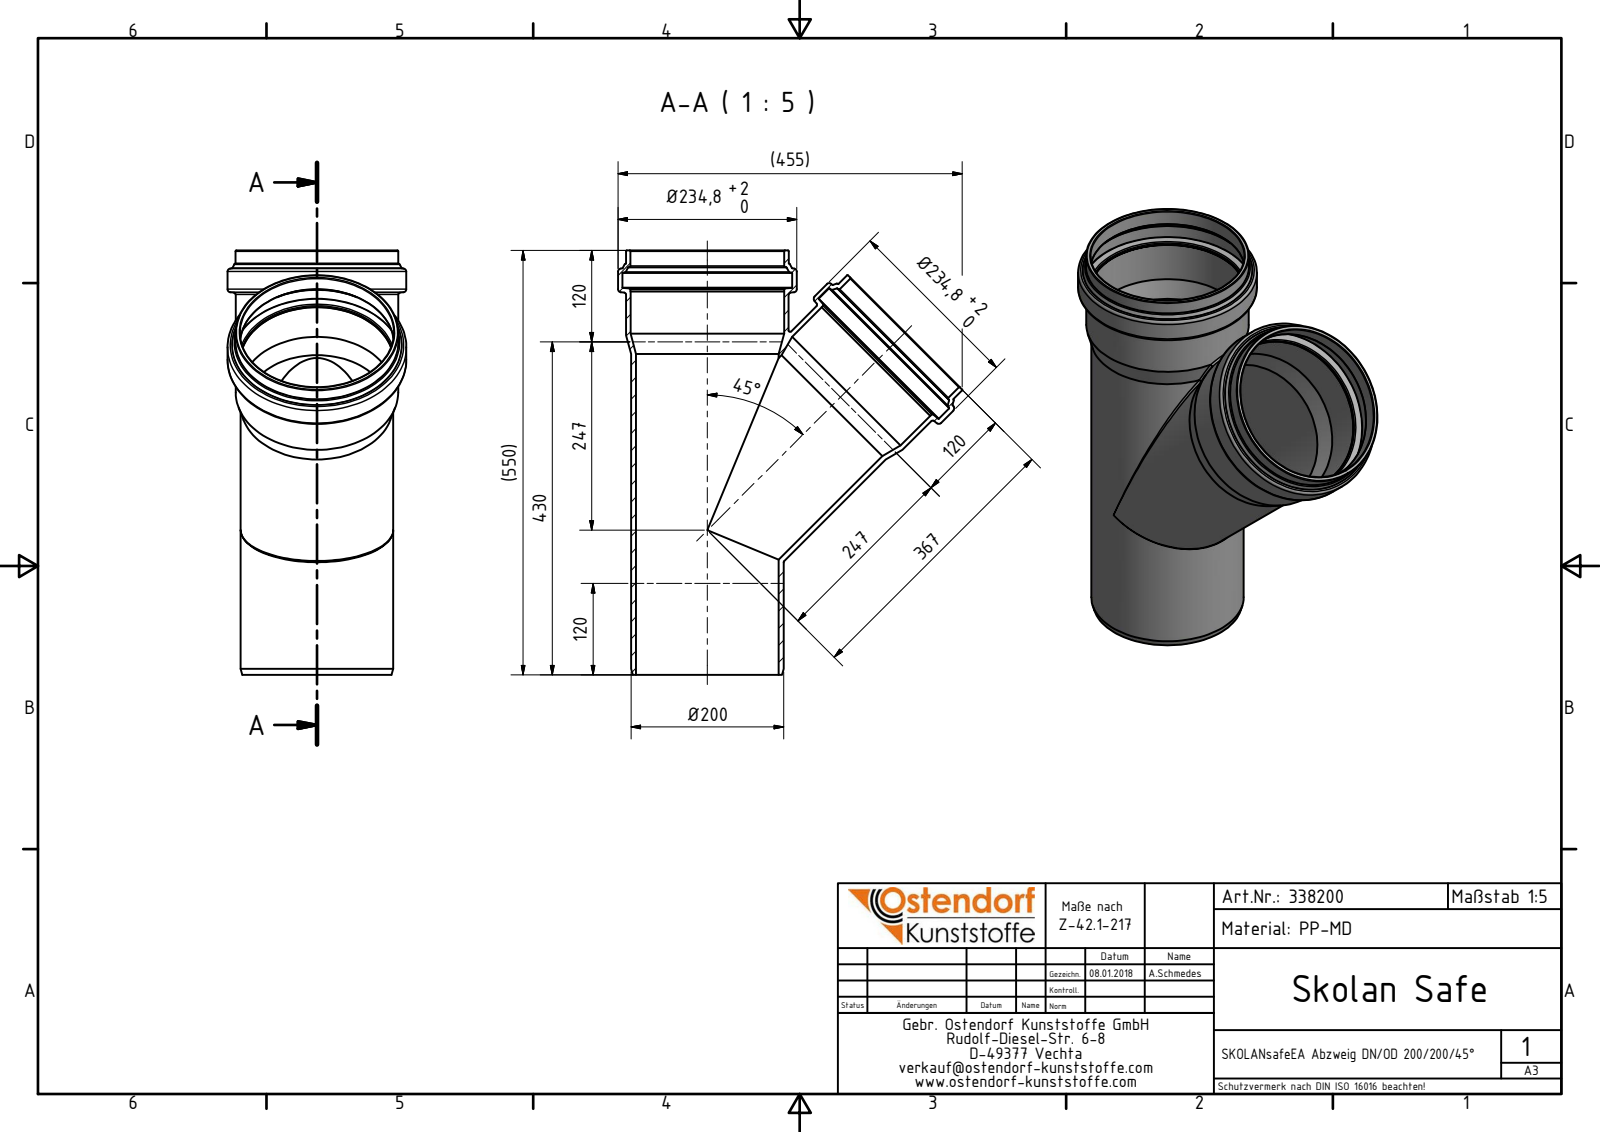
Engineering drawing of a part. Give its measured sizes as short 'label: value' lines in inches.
name: 338200 SKOLANsafeEA Abzweiger DN_OD 200_200_45°
written by: Autodesk Inventor 2016 (AUTOMOTIVE_DESIGN)
unit: in
bodies: 1 solid, 76 faces (5 planar, 18 cylindrical, 53 other)
size: 21.921 × 17.796 × 9.244
volume: 188.6 in³; area: 1 534 in²
holes: 2× ⌀7.37, 2× ⌀7.933, 2× ⌀7.945, 2× ⌀8.78
bosses: 2× ⌀9.244, 2× ⌀8.409, 2× ⌀8.398, 2× ⌀7.882
face distances: 21.921, 2.123, 19.798, 2.123
